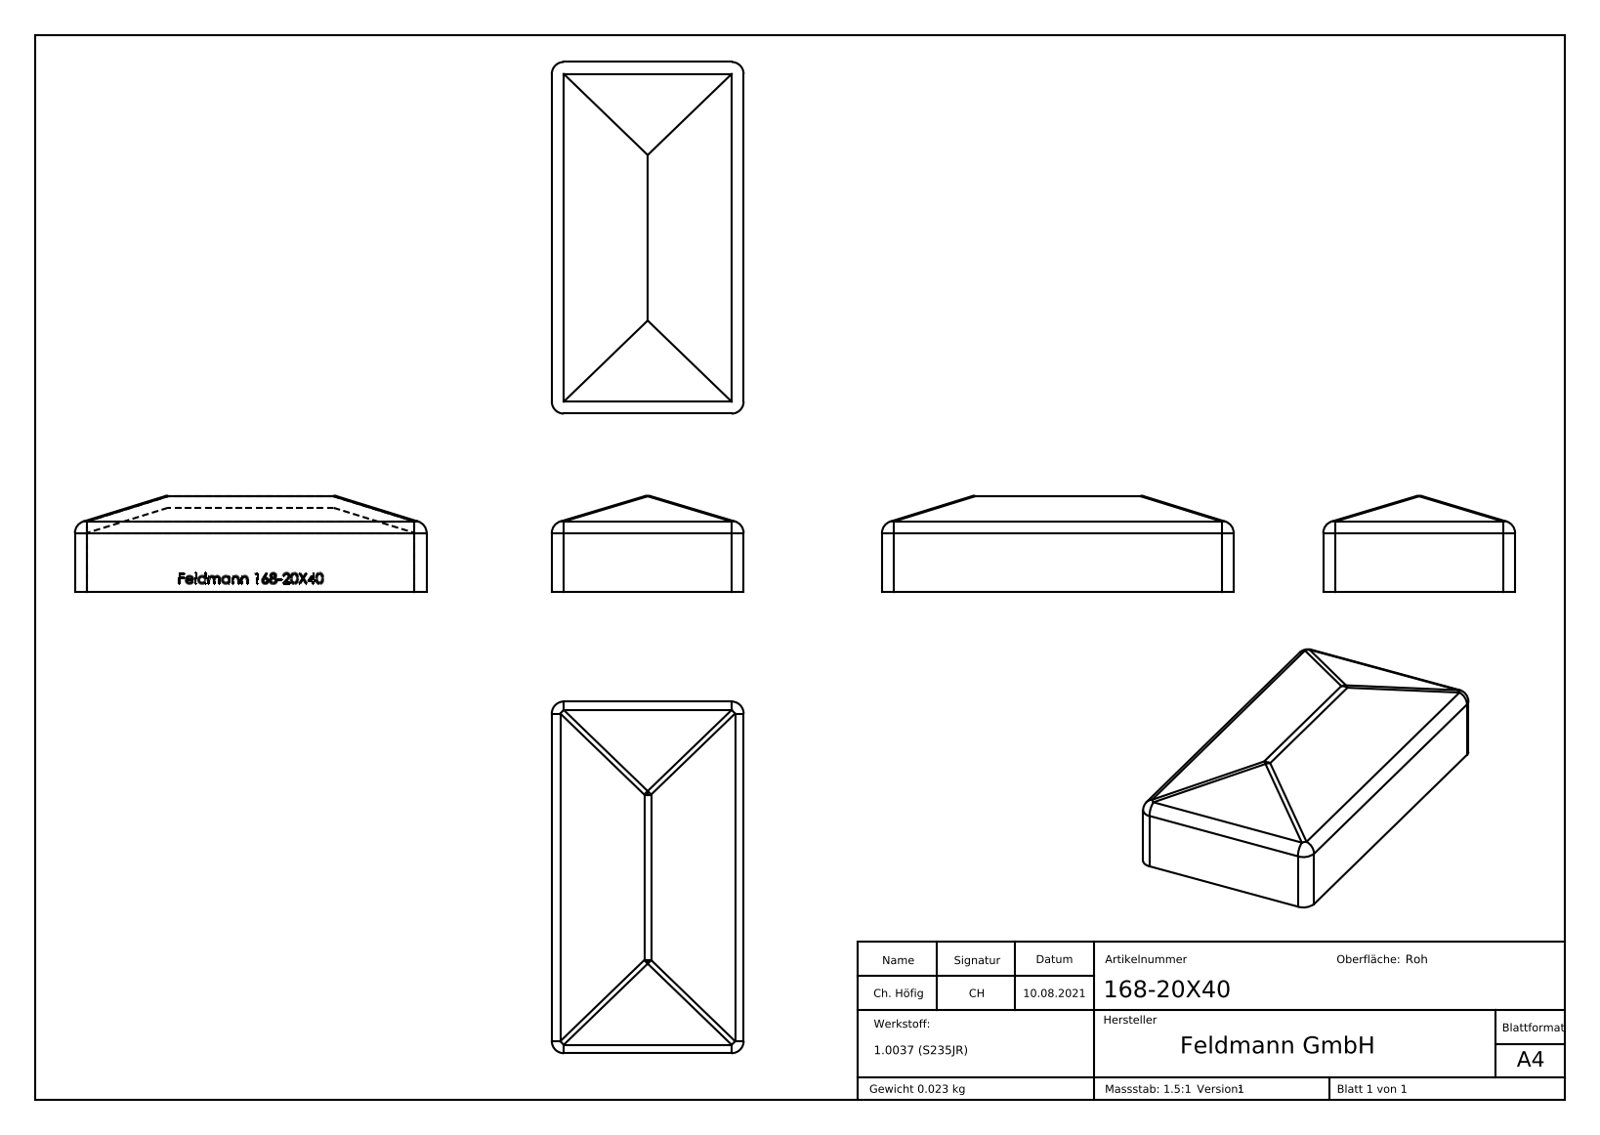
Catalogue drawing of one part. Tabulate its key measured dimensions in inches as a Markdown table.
| quantity | value |
| --- | --- |
| part name | 168-20X40 |
| STEP written by | SolidWorks 2018 (CONFIG_CONTROL_DESIGN) |
| units | inches |
| bodies | 1 solid, 263 faces (130 planar, 13 cylindrical, 120 other) |
| overall size | 1.732 × 0.945 × 0.472 |
| volume | 0.183 in³ |
| surface area | 6.512 in² |
| partial cylindrical surfaces (radius × count) | 0.059 × 13 |
| main face-to-face distances | 0.059, 0.886, 1.673, 0.945, 0.827, 1.732, 1.614, 0.055, 0.831, 0.89 |
